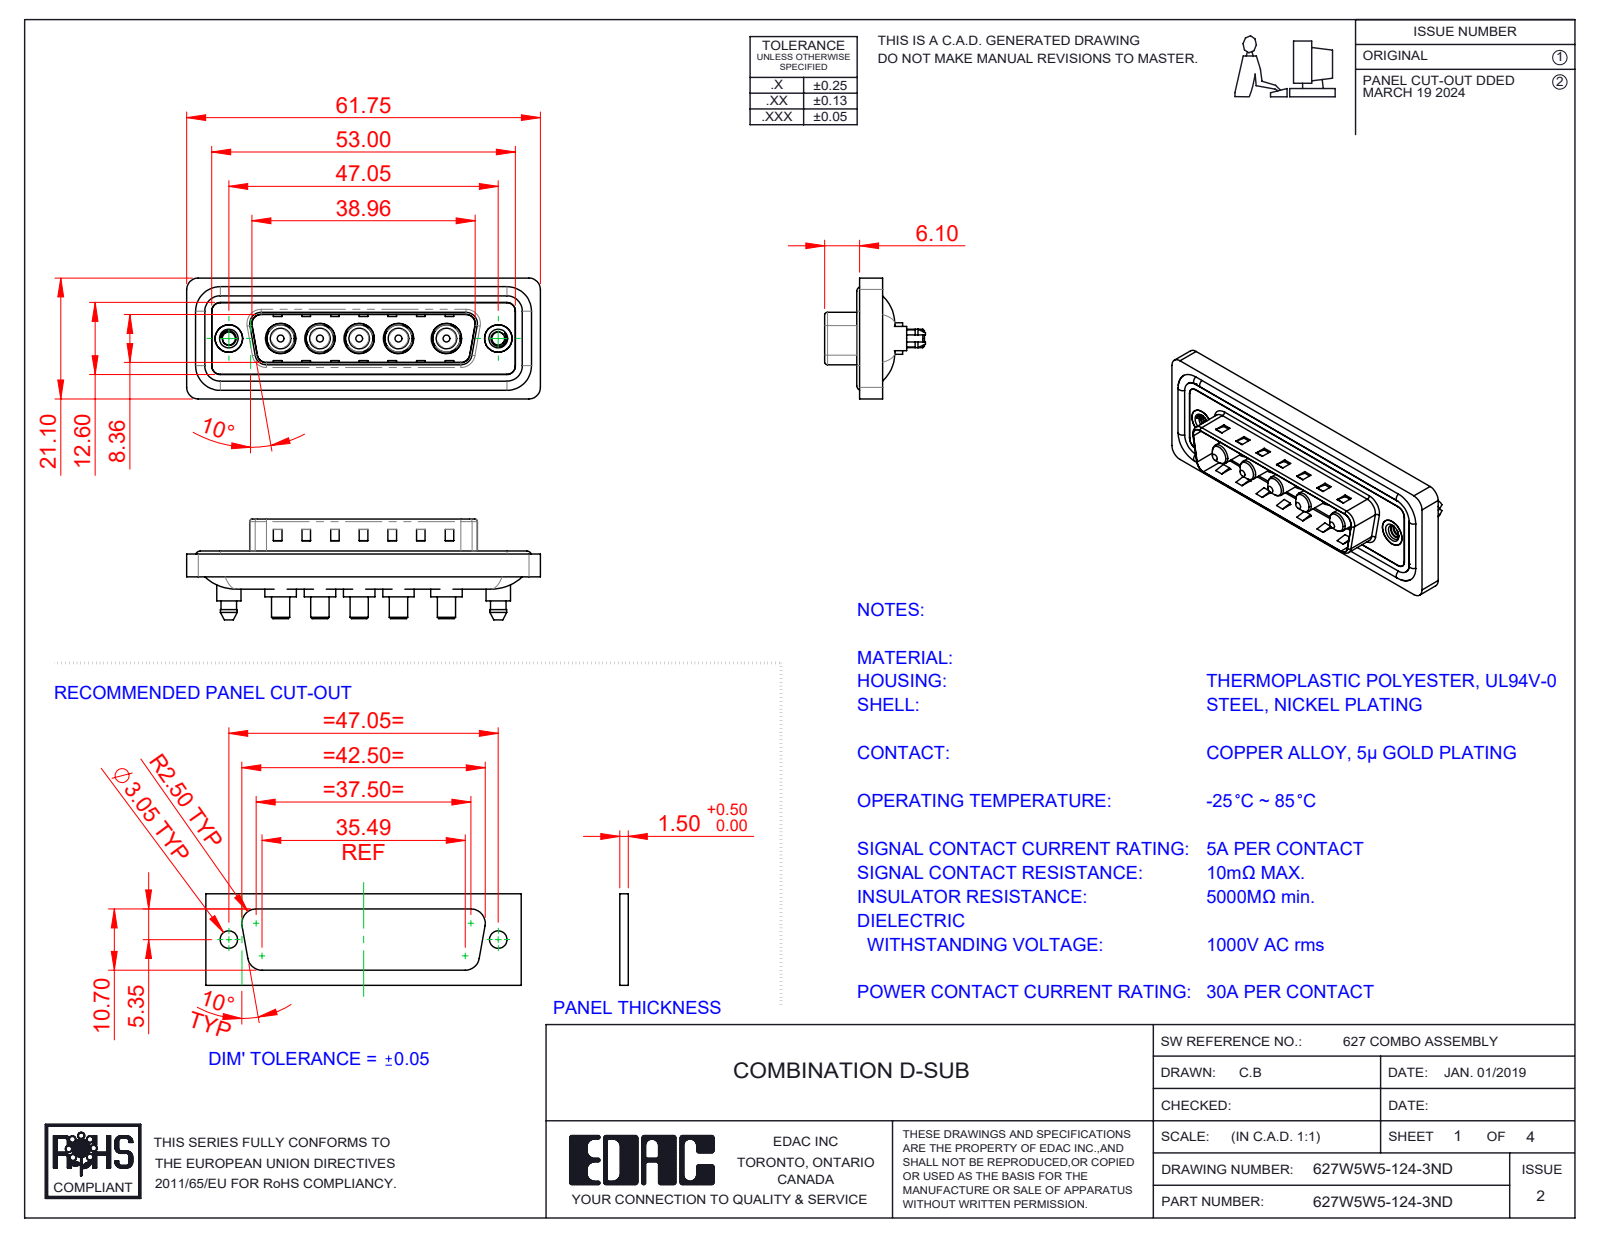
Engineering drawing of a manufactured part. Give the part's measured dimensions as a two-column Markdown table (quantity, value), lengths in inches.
| quantity | value |
| --- | --- |
| part name | Power Pin_30A S; 627Combo Waterproof Housing_25 Contacts; 627W5W5-124-3ND; 627Combo Shell Rear_25 Contacts (+4 more) |
| STEP written by | SolidWorks 2023 (CONFIG_CONTROL_DESIGN) |
| units | inches |
| bodies | 17 solids, 736 faces (275 planar, 323 cylindrical, 138 other) |
| overall size | 2.431 × 0.831 × 0.693 |
| volume | 0.466 in³ |
| surface area | 18.84 in² |
| round holes (diameter × count) | 0.191 × 5, 0.209 × 5, 0.089 × 2, 0.157 × 2, 0.189 × 2, 0.197 × 2 |
| round bosses / shafts (diameter × count) | 0.217 × 5, 0.205 × 5, 0.187 × 5, 0.148 × 5, 0.142 × 5, 0.126 × 5, 0.063 × 4, 0.213 × 2 |
| partial cylindrical surfaces (radius × count) | 0.059 × 24, 0.079 × 18, 0.063 × 10, 0.02 × 8, 0.083 × 5, 0.01 × 4, 0.024 × 4, 0.026 × 4 |
| main face-to-face distances | 0.016, 0.059, 0.122, 0.043, 0.02, 0.063, 0.114, 0.032, 0.377, 0.222 |
| hole center spacings | 0.27, 0.356, 0.541, 1.496, 0.27, 0.33, 0.33, 0.356 |
